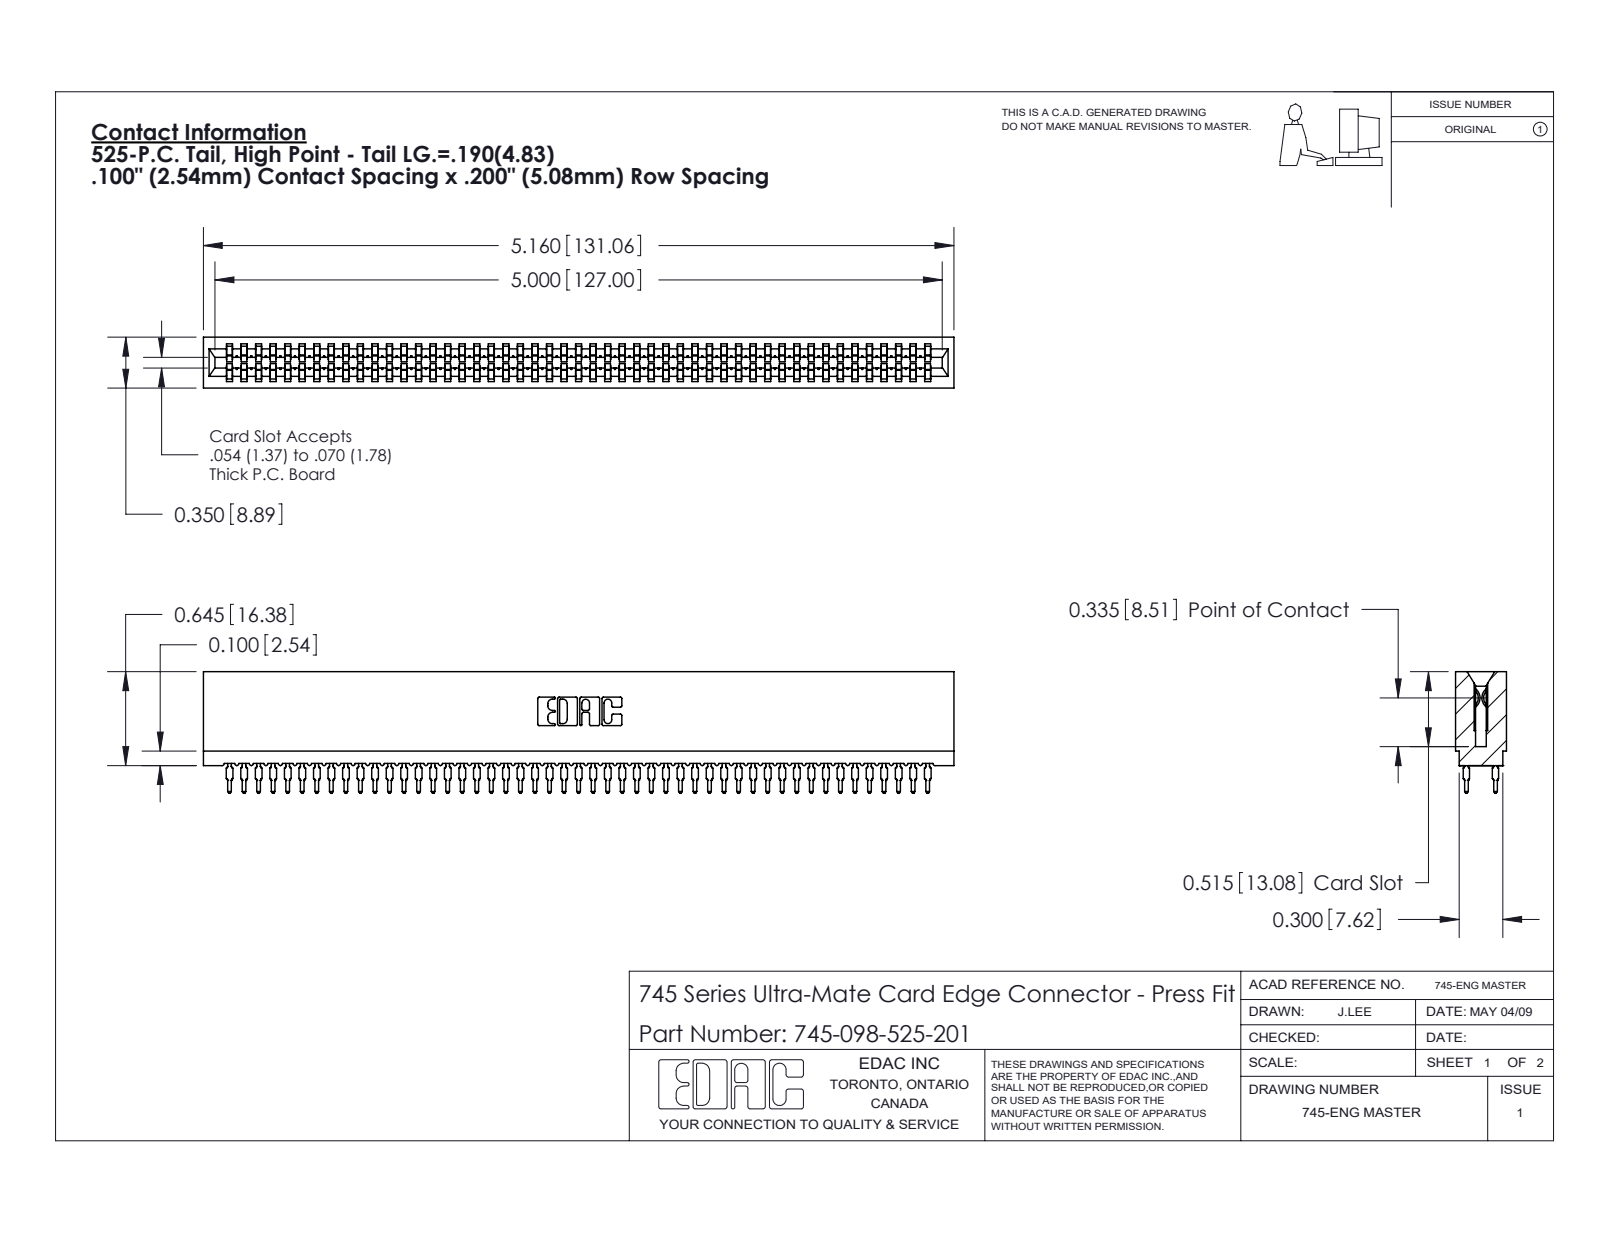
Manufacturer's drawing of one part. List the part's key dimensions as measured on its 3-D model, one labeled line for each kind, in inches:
Part name (STEP PRODUCT): 745-292-001_525; 745 Part_Insulator Option - 01; 745-098-525-201
STEP written by: SolidWorks 2020 (CONFIG_CONTROL_DESIGN)
Units: inches
Bodies: 99 solids, 8866 faces (4563 planar, 1755 cylindrical, 2548 other)
Overall size (bounding box): 5.16 × 0.836 × 0.35
Volume: 0.716 in³ · Surface area: 37.09 in²
Partial cylindrical surfaces — rounded edges, fillets, slot ends (radius × count): R0.021 ×196, R0.015 ×98, R0.01 ×22, R0.005 ×8, R0.011 ×8, R0.007 ×6, R0.031 ×6, R0.026 ×3
Main face-to-face distances: 0.35, 0.063, 0.287, 0.045, 0.305, 0.018, 0.243, 0.138, 0.212, 0.093
